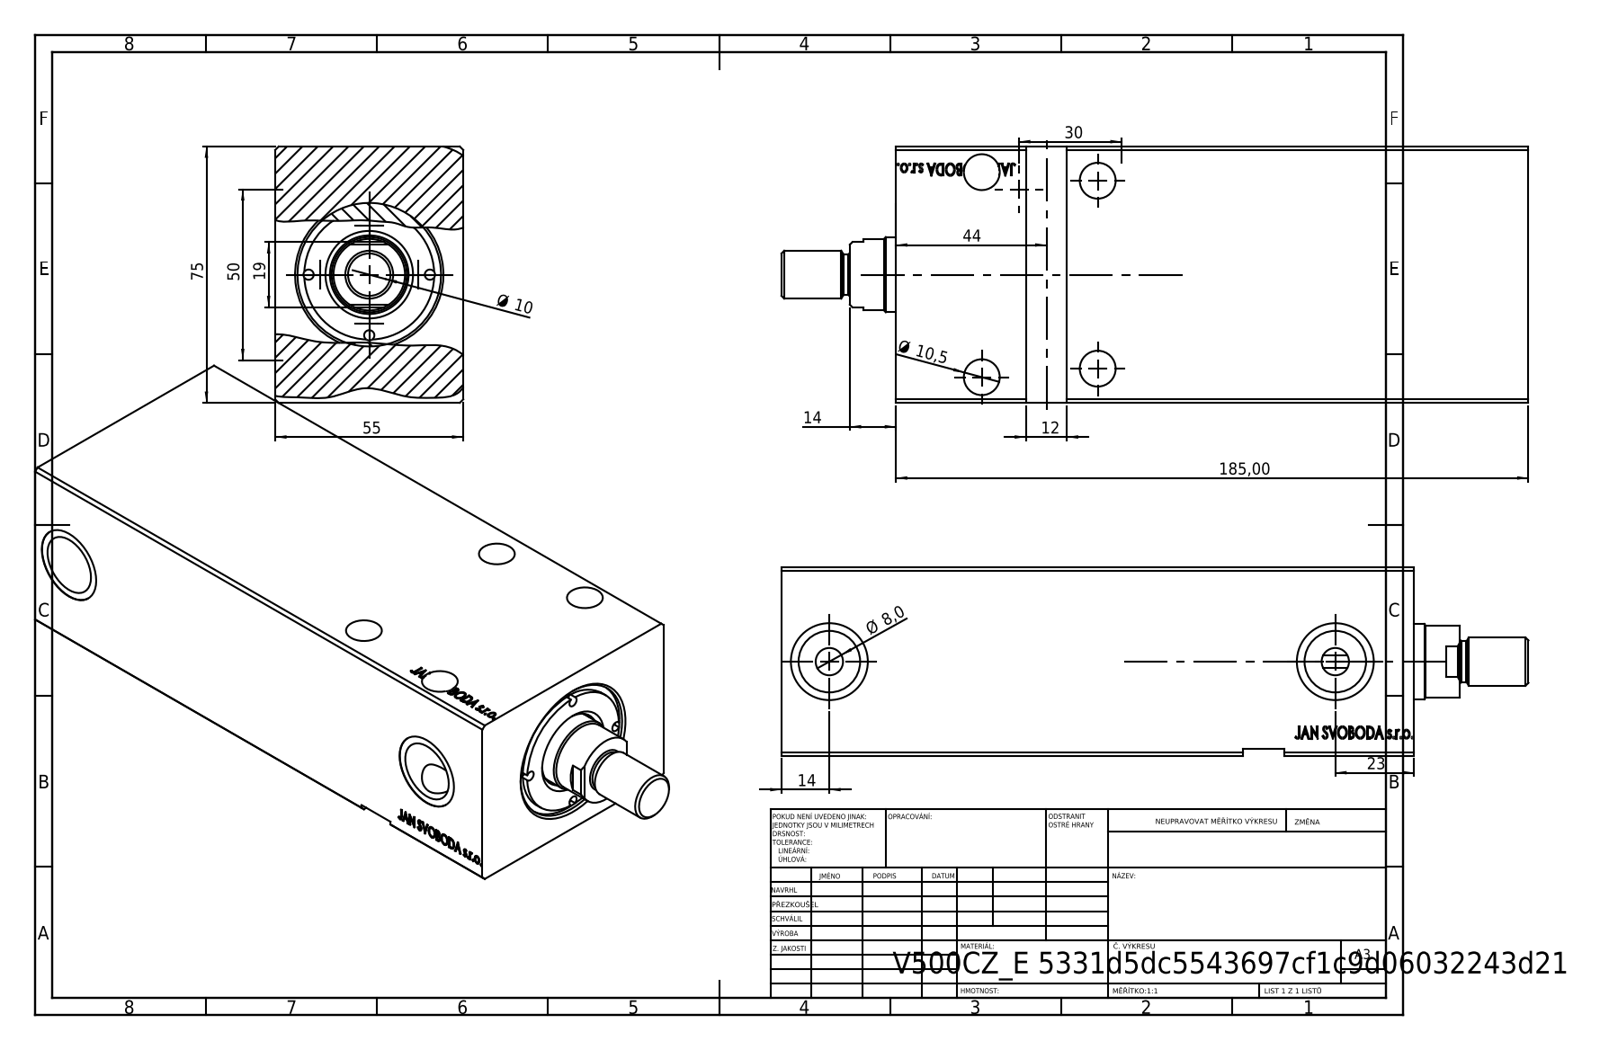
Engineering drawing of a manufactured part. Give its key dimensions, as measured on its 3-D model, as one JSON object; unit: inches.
{"part_name": "V500CZ_FM; V500CZ_VCP_E; V500CZ_E; V500CZ_VC_vysunovaci_E", "step_written_by": "SolidWorks 2019 (CONFIG_CONTROL_DESIGN)", "units": "inches", "bodies": {"solids": 4, "faces": 796, "planar": 378, "cylindrical": 58, "other": 360}, "overall_size": [8.602, 2.953, 2.165], "volume_in3": 42.2, "surface_area_in2": 155.2, "round_holes": [[0.118, 4], [0.413, 4], [0.315, 2], [0.709, 2], [0.886, 2], [0.394, 1], [0.866, 1], [0.906, 1], [1.26, 1], [1.417, 1], [1.654, 1]], "round_bosses_or_shafts": [[1.496, 1], [0.824, 1], [0.551, 1], [0.472, 1]], "face_to_face_distances": [2.165, 2.953, 7.283, 6.102, 1.181, 7.276, 1.173, 0.465, 5.638, 6.811], "hole_center_spacings": [0.699, 0.988, 1.339, 1.398, 2.628, 2.165, 2.362, 5.827]}
